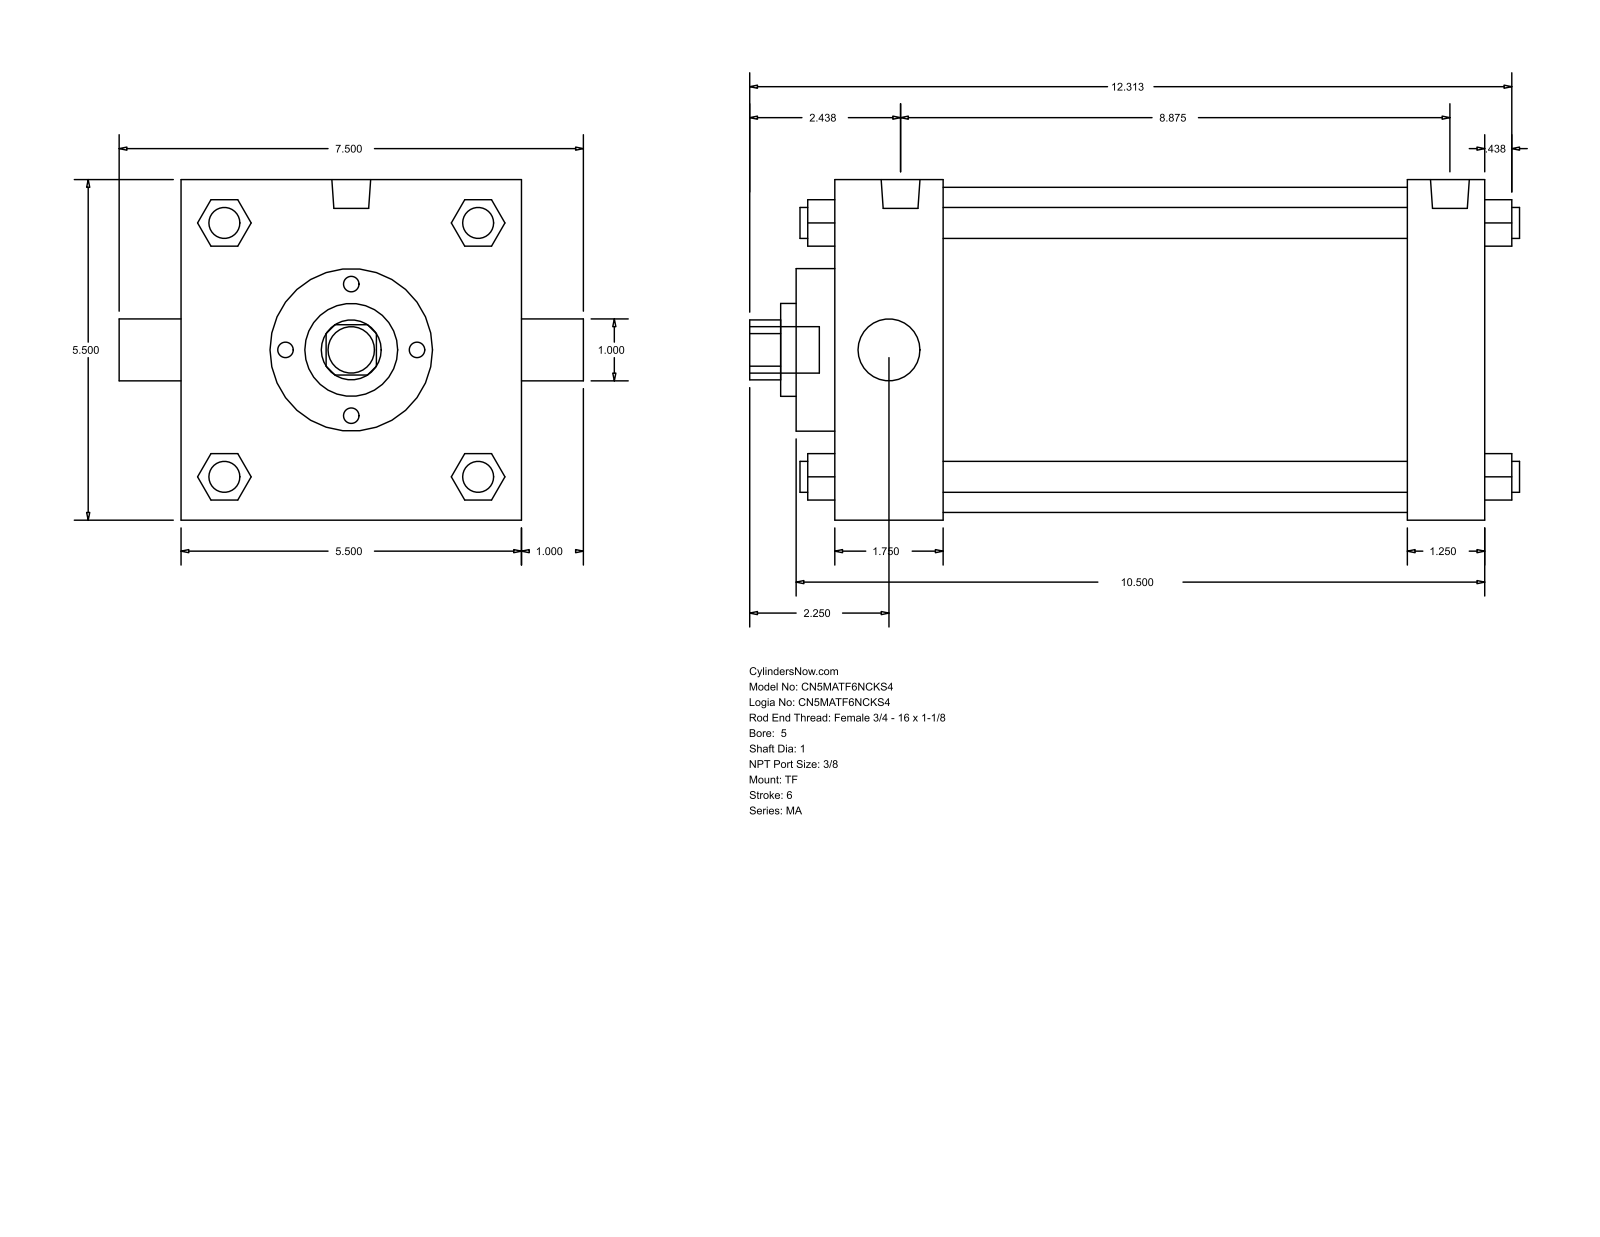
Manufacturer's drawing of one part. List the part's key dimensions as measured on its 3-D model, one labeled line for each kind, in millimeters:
Part name (STEP PRODUCT): MA_TF__0500_1
STEP written by: GSSL Pune (CONFIG_CONTROL_DESIGN)
Units: millimetres
Bodies: 0 solids, 122 faces (93 planar, 29 cylindrical, 0 other)
Overall size (bounding box): 315.91 × 190.5 × 139.7
Round holes (diameter × count): ⌀25.4 ×2, ⌀38.1 ×1, ⌀66.67 ×1, ⌀133.35 ×1
Round bosses / shafts (diameter × count): ⌀12.7 ×4, ⌀11.11 ×3, ⌀15.93 ×2, ⌀19.05 ×1
Partial cylindrical surfaces — rounded edges, fillets, slot ends (radius × count): R12.29 ×1
Main face-to-face distances: 139.7, 266.7, 190.5, 234.96, 31.74, 44.46, 222.24, 15.87, 60.33, 250.83
